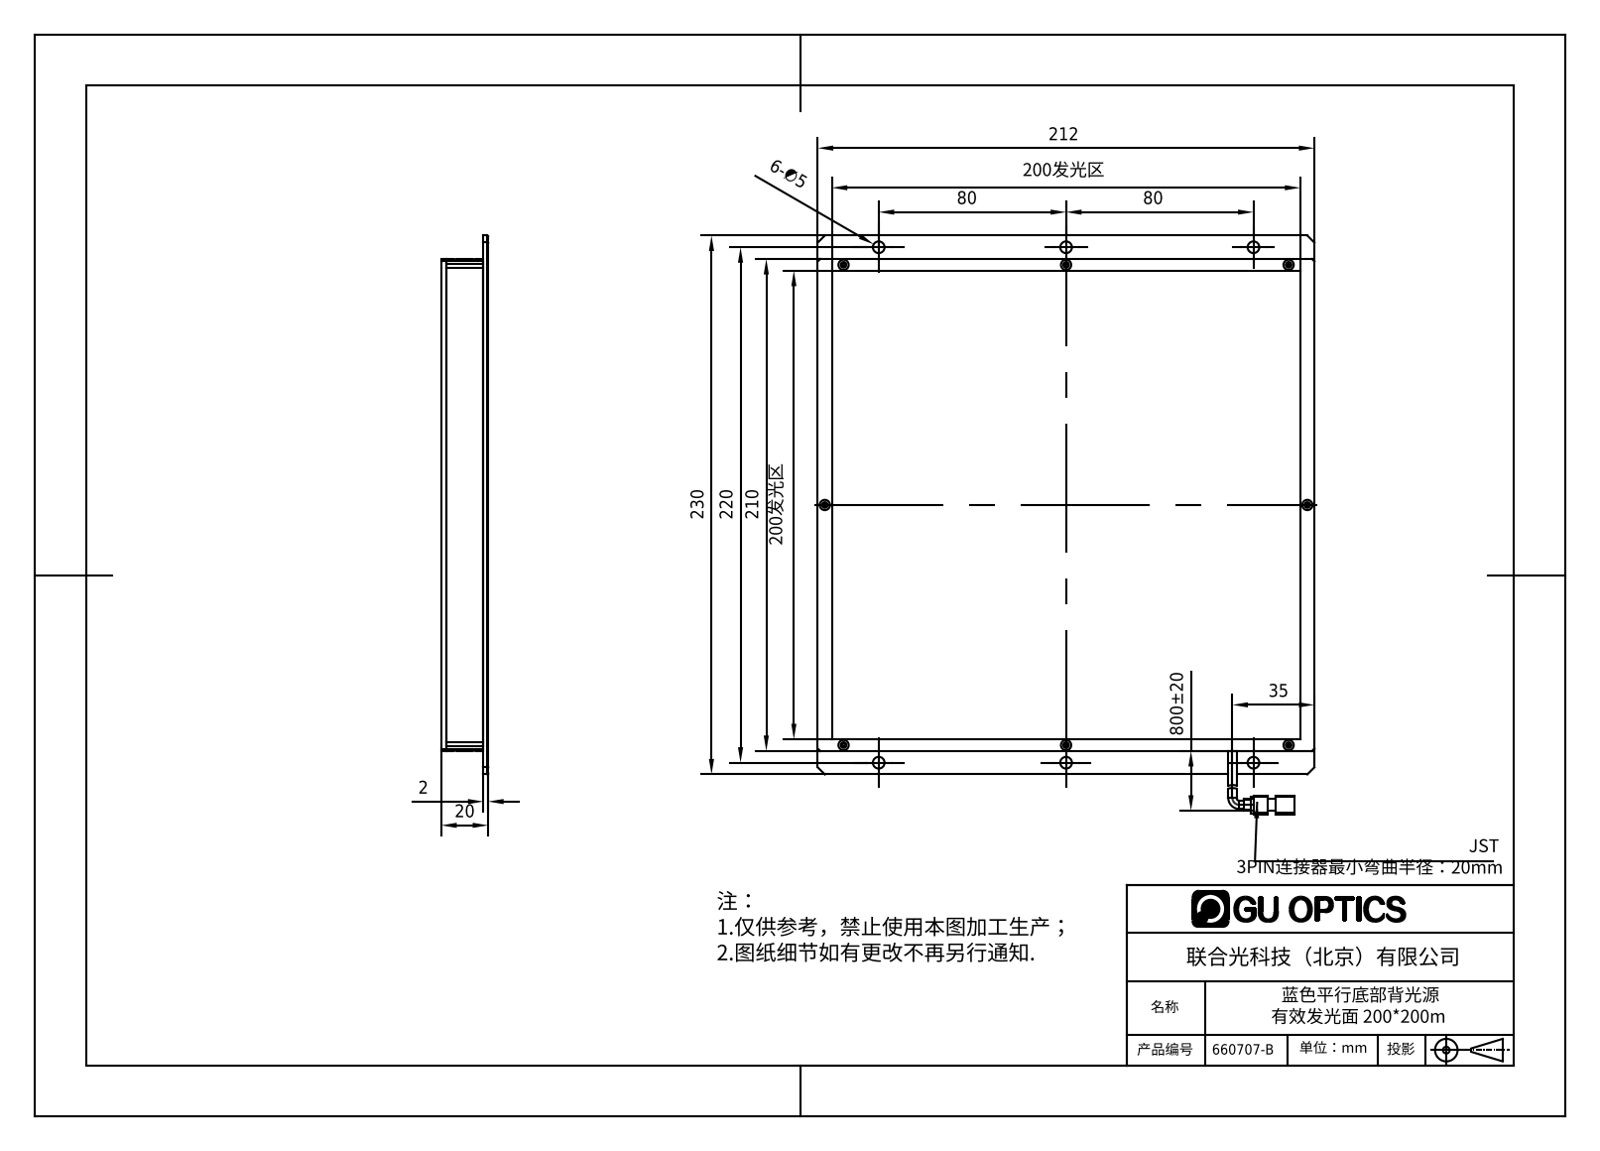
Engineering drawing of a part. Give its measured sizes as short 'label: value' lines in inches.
name: 660707-B
written by: SolidWorks 2016 (AUTOMOTIVE_DESIGN)
unit: in
bodies: 8 solids, 520 faces (197 planar, 149 cylindrical, 174 other)
size: 9.724 × 8.346 × 0.882
volume: 15.96 in³; area: 353.9 in²
holes: 16× ⌀0.063, 16× ⌀0.094, 6× ⌀0.197
bosses: 2× ⌀0.138
rounds: 8× R0.02, 4× R0.039, 2× R0.079, 1× R0.063
face distances: 0.079, 0.709, 0.63, 0.083, 0.791, 0.713, 0.236, 8.11, 0.197, 7.874
hole spacings: 3.74, 8.11, 0.432, 0.66, 1.081, 3.15, 3.163, 3.752
